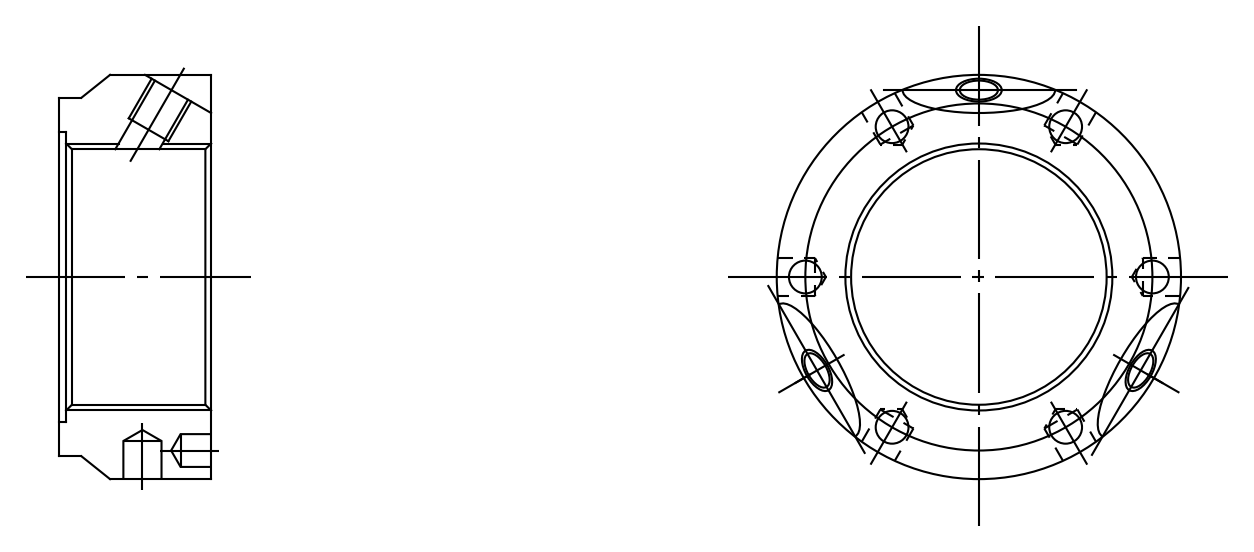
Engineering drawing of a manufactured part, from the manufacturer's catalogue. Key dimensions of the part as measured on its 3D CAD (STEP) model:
Part name (STEP PRODUCT): FKD FKNA35
STEP written by: Autodesk Inventor LT (CONFIG_CONTROL_DESIGN)
Units: millimetres
Bodies: 1 solid, 44 faces (6 planar, 25 cylindrical, 13 other)
Overall size (bounding box): 53 × 53 × 20
Volume: 21 690 mm³ · Surface area: 9 014 mm²
Round holes (diameter × count): ⌀4.3 ×6, ⌀5 ×3, ⌀6.1 ×3, ⌀4.92 ×2, ⌀4.92 ×1, ⌀35 ×1, ⌀38 ×1
Round bosses / shafts (diameter × count): ⌀53 ×1, ⌀47 ×1
Partial cylindrical surfaces — rounded edges, fillets, slot ends (radius × count): R20 ×3
Main face-to-face distances: 20, 1.5, 18.5
Hole centre spacings: 22.75, 39.4, 39.41, 45.5, 22.76
